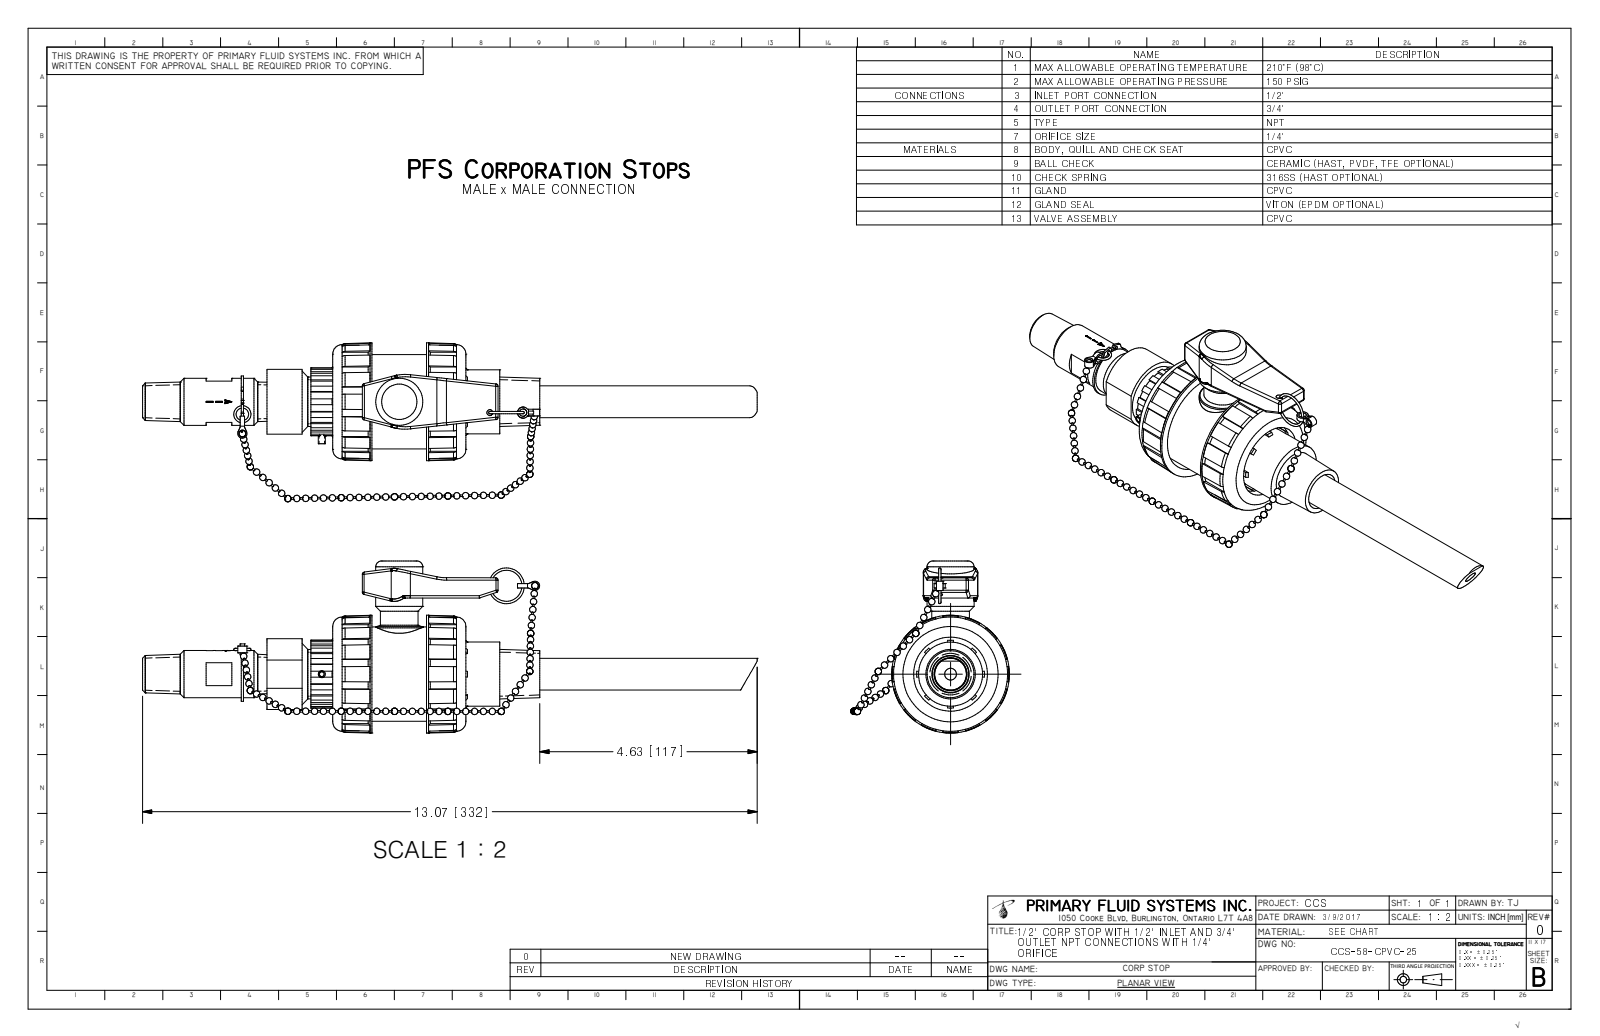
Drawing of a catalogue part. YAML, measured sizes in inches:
part_name: "CCS-58-CPVC-25_R0"
step_written_by: "Autodesk Inventor 2009 (AUTOMOTIVE_DESIGN)"
units: inches
bodies: {solids: 1, faces: 616, planar: 226, cylindrical: 144, other: 246}
overall_size: [13.069, 3.65, 3.372]
volume: 19.04
surface_area: 111
round_holes:
  - {diameter: 0.079, count: 1}
  - {diameter: 0.25, count: 1}
  - {diameter: 0.469, count: 1}
  - {diameter: 0.56, count: 1}
  - {diameter: 1.57, count: 1}
  - {diameter: 2.16, count: 1}
round_bosses_or_shafts:
  - {diameter: 1, count: 2}
  - {diameter: 2.5, count: 1}
  - {diameter: 2, count: 1}
  - {diameter: 1.801, count: 1}
  - {diameter: 1.36, count: 1}
  - {diameter: 1.094, count: 1}
  - {diameter: 0.8, count: 1}
  - {diameter: 0.675, count: 1}
partial_cylinders:
  - {radius: 0.05, count: 21}
  - {radius: 1, count: 3}
  - {radius: 0.043, count: 2}
  - {radius: 0.157, count: 2}
  - {radius: 0.351, count: 1}
  - {radius: 0.463, count: 1}
  - {radius: 0.499, count: 1}
  - {radius: 0.614, count: 1}
face_to_face_distances: [0.205, 2.625, 0.835, 1.995, 0.63, 1.79, 0.465, 2.83, 2.42, 1.16]
hole_center_spacings: [0.535]
